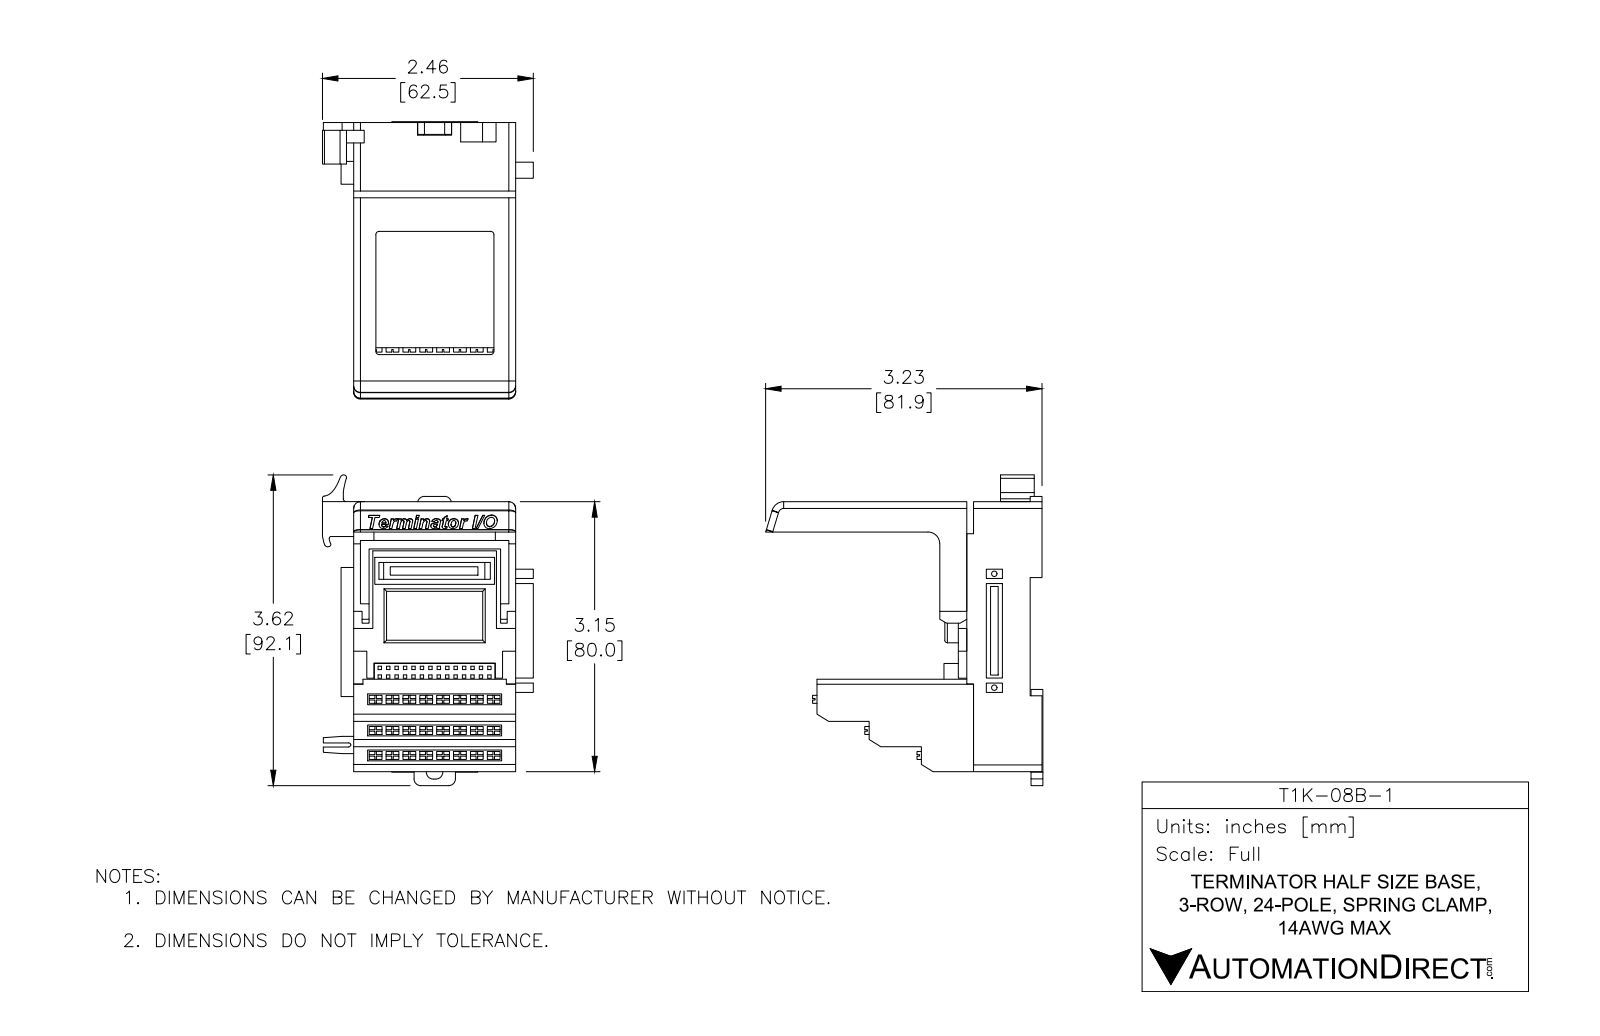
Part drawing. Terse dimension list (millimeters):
name: T1K-08B-1
written by: SolidWorks 2013 (AUTOMOTIVE_DESIGN)
unit: mm
bodies: 12 solids, 1028 faces (867 planar, 56 cylindrical, 105 other)
size: 92.07 × 82.17 × 62.5
volume: 139 888 mm³; area: 42 612 mm²
holes: 2× ⌀1.6
bosses: 2× ⌀1.5
rounds: 14× R1, 13× R2, 8× R0.75, 2× R2.06, 1× R0.83, 1× R2.02, 1× R2.04, 1× R3.5
face distances: 2, 48, 3.5, 18.8, 52.6, 16.8, 22.3, 20.3, 27.4, 80
hole spacings: 33.75
